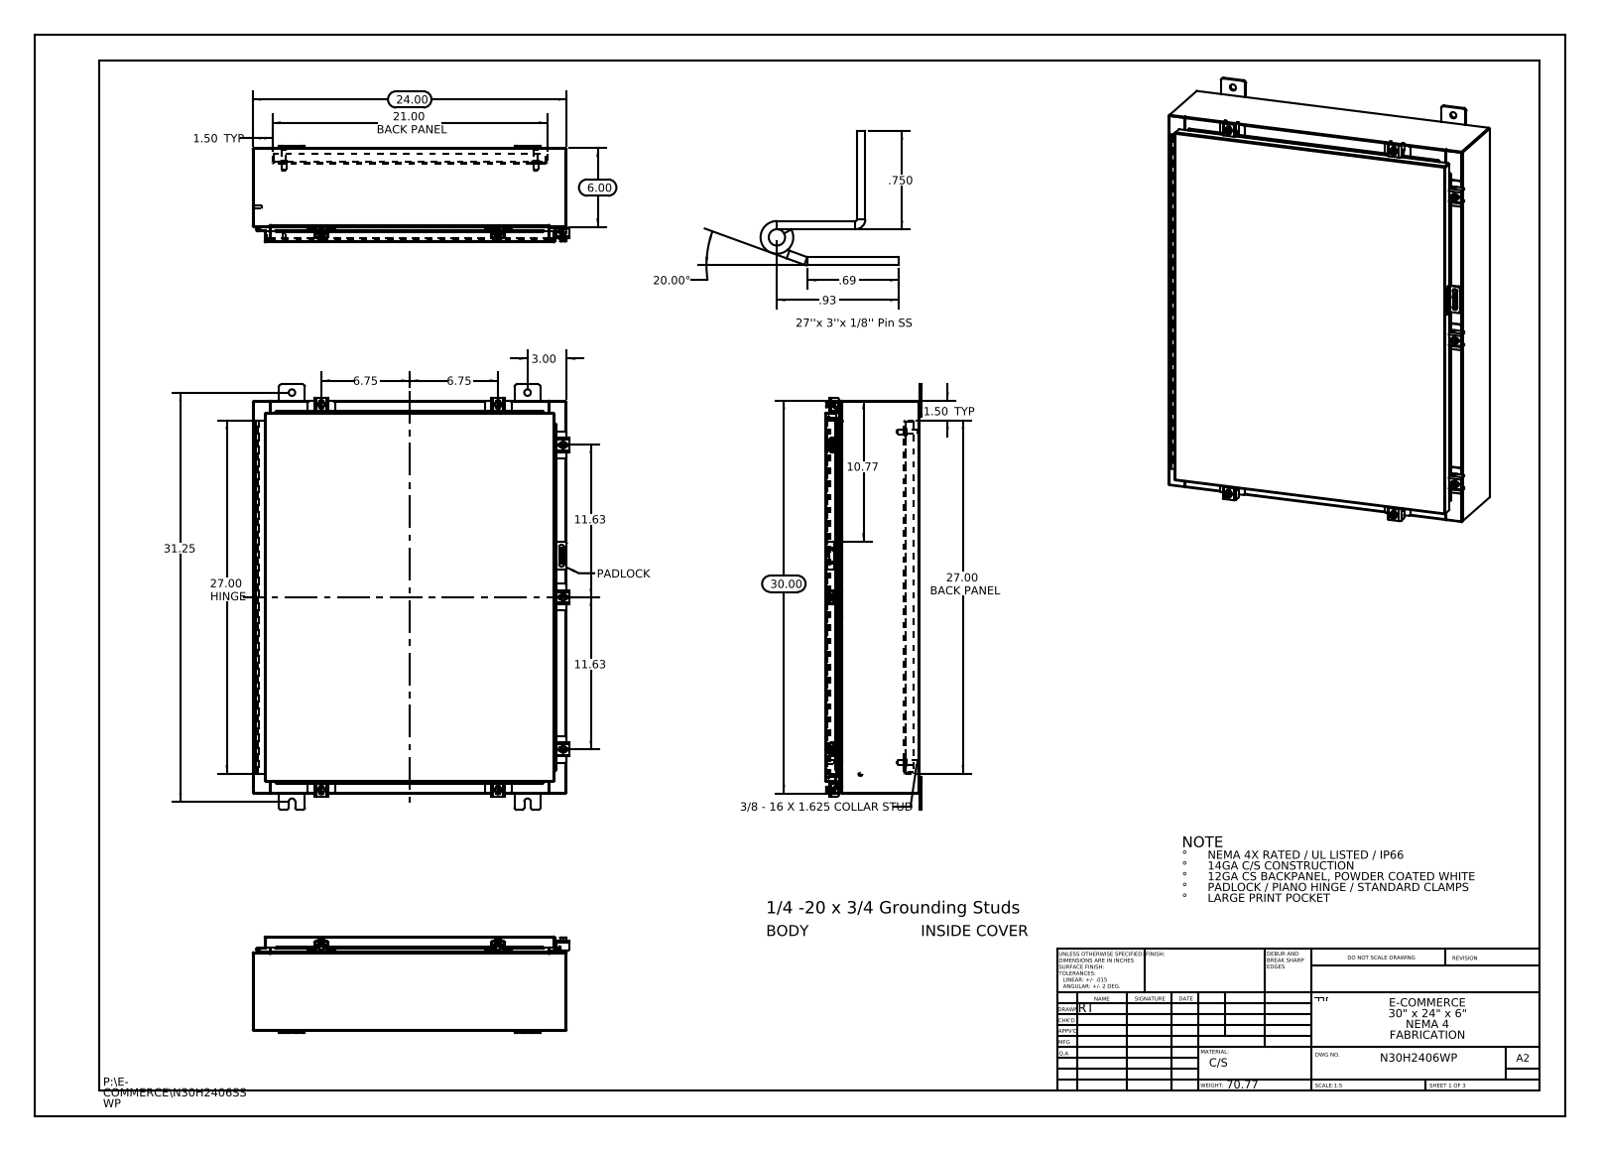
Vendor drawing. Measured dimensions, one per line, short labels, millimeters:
name: N30H2406SSWP 22104005_DEFAULT; N30H2406SSWP 22101002; N30H2406SSWP Clamp Bracket; N30H2406SSWP Padlock Hasp (+8 more)
written by: SolidWorks 2013 (CONFIG_CONTROL_DESIGN)
unit: mm
bodies: 54 solids, 2016 faces (1062 planar, 838 cylindrical, 116 other)
size: 825.5 × 615 × 187.7
volume: 4 077 000 mm³; area: 3 993 000 mm²
holes: 8× ⌀12.7, 7× ⌀5.4, 7× ⌀6.6, 2× ⌀3.2, 1× ⌀3.2
bosses: 8× ⌀6.4, 7× ⌀12.7, 7× ⌀10.1, 4× ⌀15.9, 4× ⌀9.5, 4× ⌀8.4, 2× ⌀8, 2× ⌀6
rounds: 34× R1.5, 27× R0.3, 24× R4.8, 21× R2.2, 14× R3, 14× R3.6, 11× R1.3, 10× R2
face distances: 1.9, 181, 179.1, 182.9, 2.6, 25.4, 27.3, 153.7, 155.6, 29.9
hole spacings: 698.5, 809.7, 47.2, 57.8, 59.1, 61.5, 90.4, 90.4
